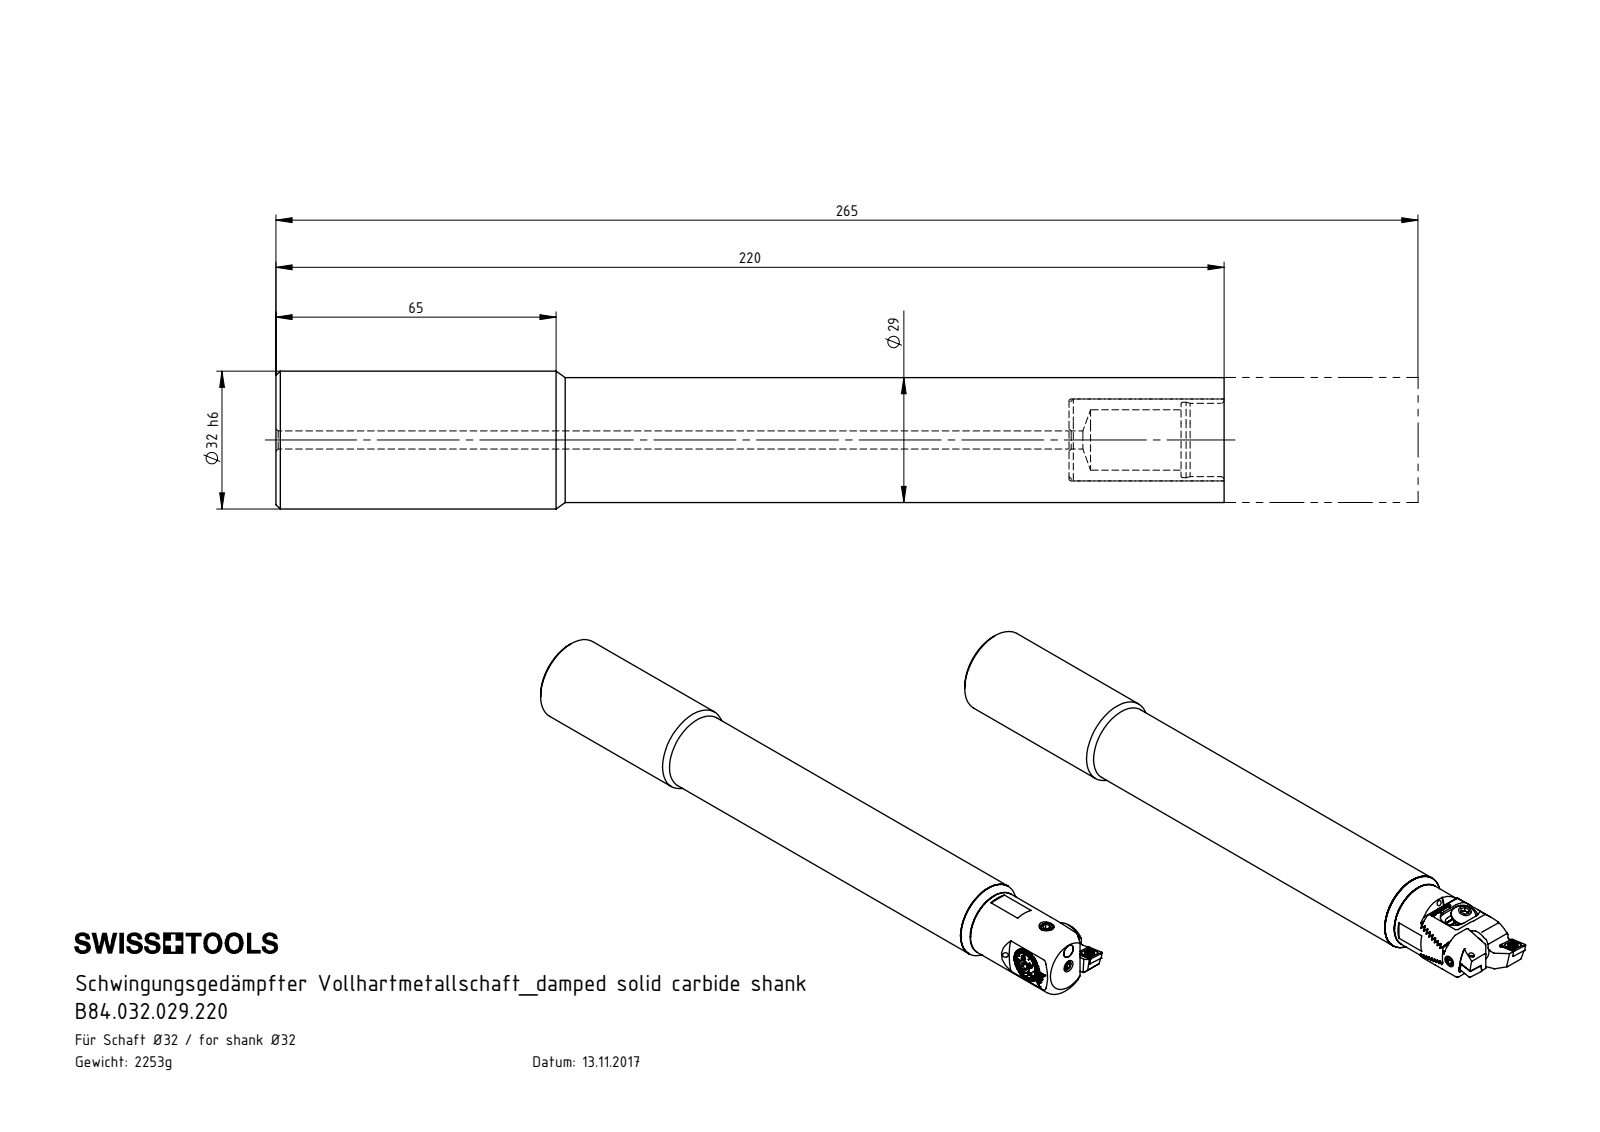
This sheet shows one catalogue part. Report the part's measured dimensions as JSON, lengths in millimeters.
{"part_name": "B84.032.029.220; U32-HP5.029.220_A; HP5-Z25.030.045_A; WCA-ER2.001.006_A (+8 more)", "step_written_by": "SolidWorks 2017 (CONFIG_CONTROL_DESIGN)", "units": "millimeters", "bodies": {"solids": 19, "faces": 1088, "planar": 510, "cylindrical": 274, "other": 304}, "overall_size": [265, 32, 32], "volume_mm3": 167210, "surface_area_mm2": 45730, "round_holes": [[2, 6], [4.2, 3], [1.6, 2], [2.05, 2], [2.8, 2], [3.85, 2], [6, 2], [2.5, 1], [3.3, 1], [3.5, 1], [5.3, 1], [10.6, 1]], "round_bosses_or_shafts": [[9.5, 2], [5, 2], [4, 2], [3.4, 2], [2.5, 2], [32, 1], [29, 1], [25, 1]], "partial_cylinders_radius": [[0.12, 18], [0.5, 18], [0.12, 16], [0.21, 12], [0.36, 10], [2, 4], [2.8, 4], [5, 4]], "face_to_face_distances": [1.43, 3, 220, 223, 2.86, 39, 184, 36, 1.39, 10], "hole_center_spacings": [3.91, 4.01, 7, 19.06, 19.15, 21.97, 13.52, 15.9]}
